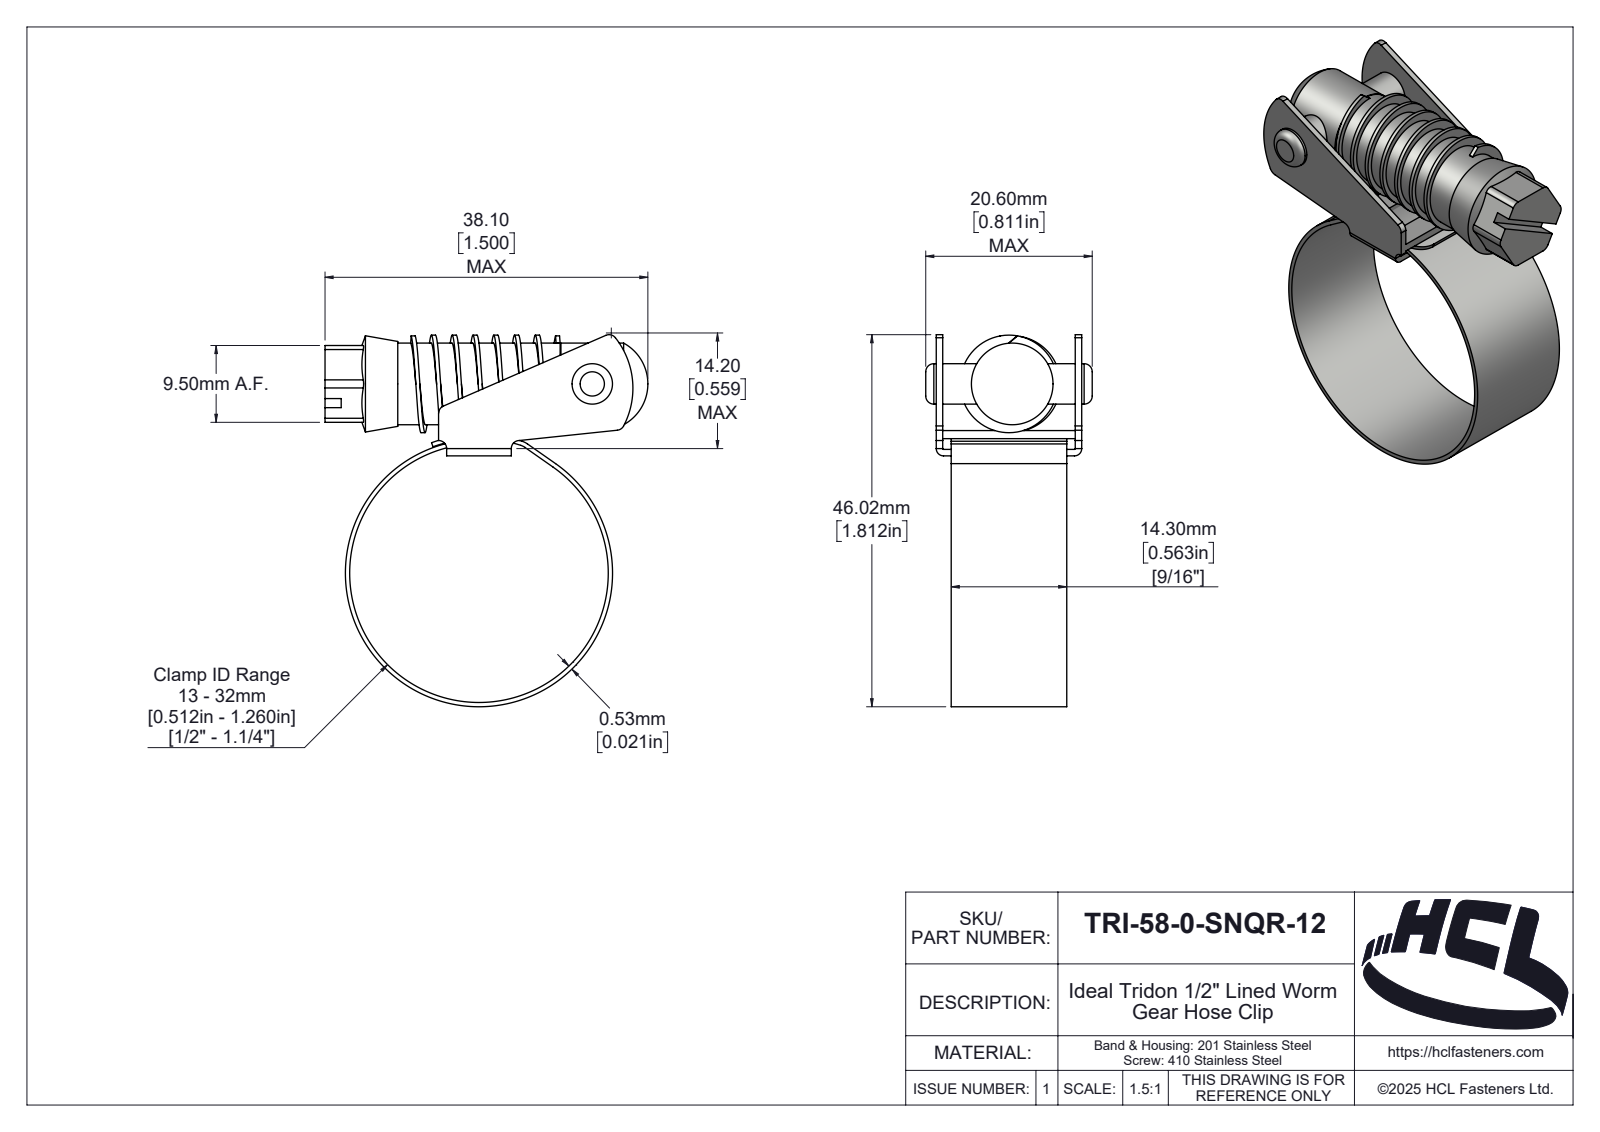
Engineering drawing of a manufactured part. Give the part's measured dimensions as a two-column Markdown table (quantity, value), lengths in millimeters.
| quantity | value |
| --- | --- |
| part name | TRI-58-0-SNQR-12 |
| STEP written by | SolidWorks 2025 (AUTOMOTIVE_DESIGN) |
| units | millimeters |
| bodies | 5 solids, 222 faces (44 planar, 112 cylindrical, 66 other) |
| overall size | 46.02 × 38.1 × 20.6 |
| volume | 4 642 mm³ |
| surface area | 7 163 mm² |
| round holes (diameter × count) | 5 × 1, 32 × 1 |
| round bosses / shafts (diameter × count) | 33.06 × 1, 10.1 × 1 |
| partial cylindrical surfaces (radius × count) | 1 × 11, 0.1 × 2, 0.9 × 2, 3 × 2, 0.46 × 1, 1.89 × 1, 2 × 1, 2.35 × 1 |
| main face-to-face distances | 0.8, 17.2, 18, 16.4, 1, 1.85, 16.15, 1.05, 15.35, 3.13 |
| hole center spacings | 27.28 |
